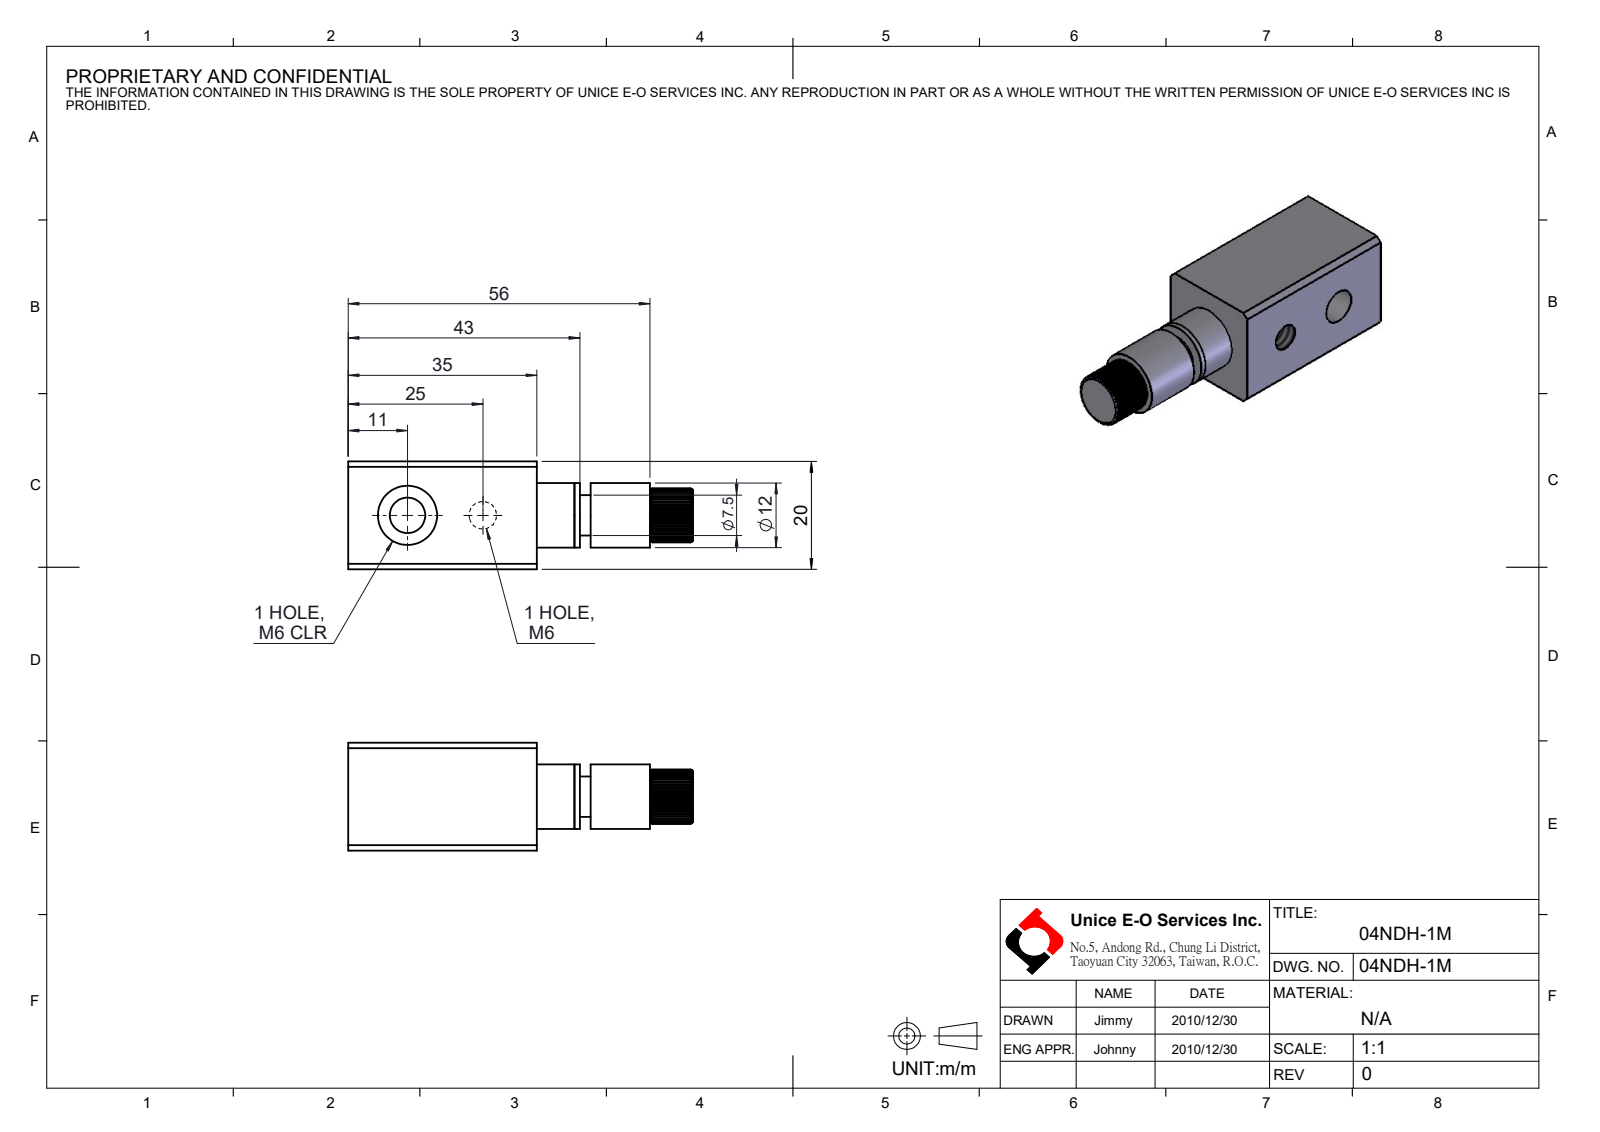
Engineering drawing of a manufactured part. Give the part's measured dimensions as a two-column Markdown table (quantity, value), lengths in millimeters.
| quantity | value |
| --- | --- |
| part name | 04NDH-1M |
| STEP written by | SolidWorks 2016 (CONFIG_CONTROL_DESIGN) |
| units | millimeters |
| bodies | 4 solids, 268 faces (121 planar, 137 cylindrical, 10 other) |
| overall size | 64 × 20 × 20 |
| volume | 15 014 mm³ |
| surface area | 6 417 mm² |
| round holes (diameter × count) | 3.3 × 1, 4.6 × 1, 5 × 1, 6.6 × 1, 7.5 × 1, 7.7 × 1, 11 × 1 |
| round bosses / shafts (diameter × count) | 12 × 1, 4 × 1 |
| partial cylindrical surfaces (radius × count) | 5 × 1 |
| main face-to-face distances | 20, 35, 21, 7, 14, 56, 10, 42, 8, 6.72 |
| hole center spacings | 14 |
